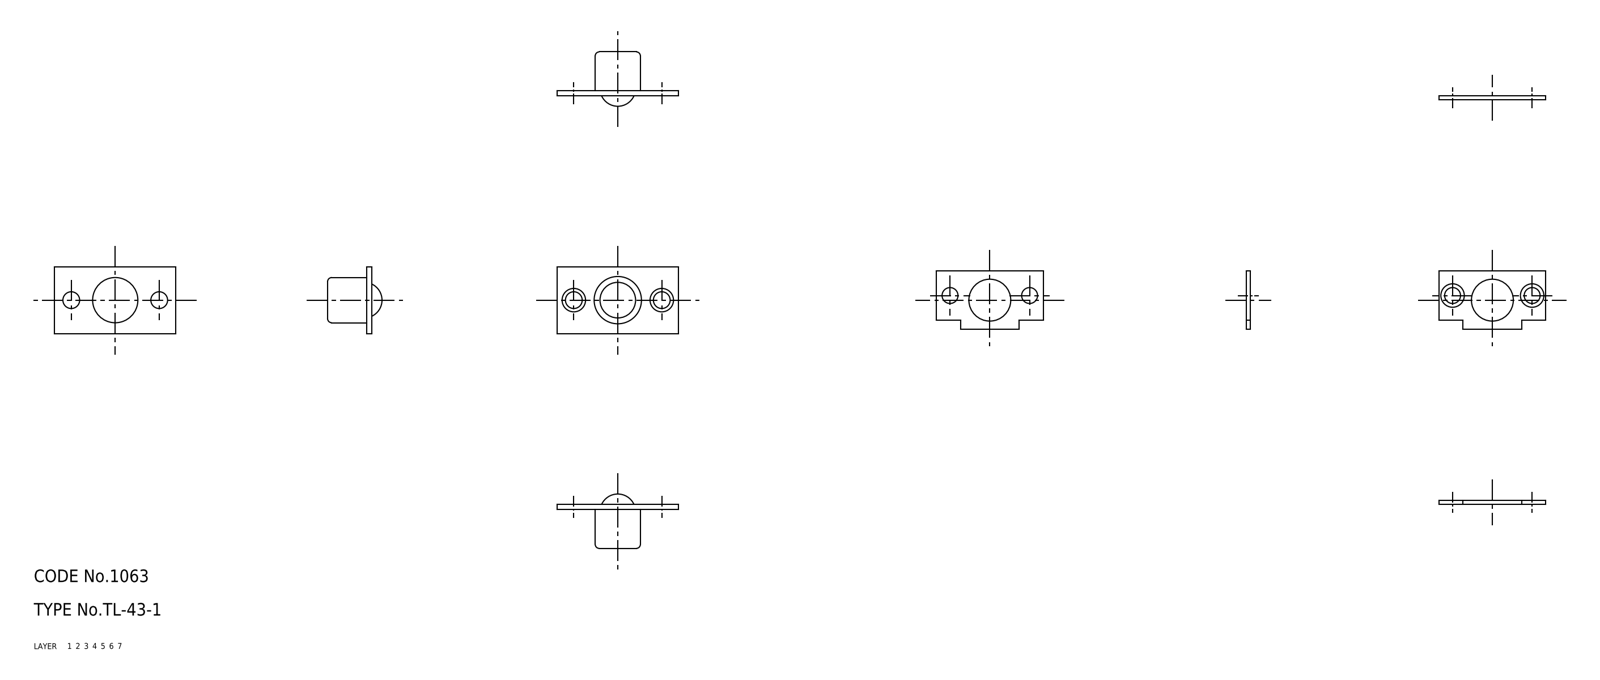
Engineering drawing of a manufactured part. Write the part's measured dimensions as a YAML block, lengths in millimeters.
part_name: "keeper; bracket; ball; TL_43_1_14104_36"
step_written_by: "CADfix (AUTOMOTIVE_DESIGN)"
units: millimeters
bodies: {solids: 3, faces: 50, planar: 0, cylindrical: 0, other: 50}
overall_size: [36.72, 29, 16]
volume: 1179
surface_area: 2460
